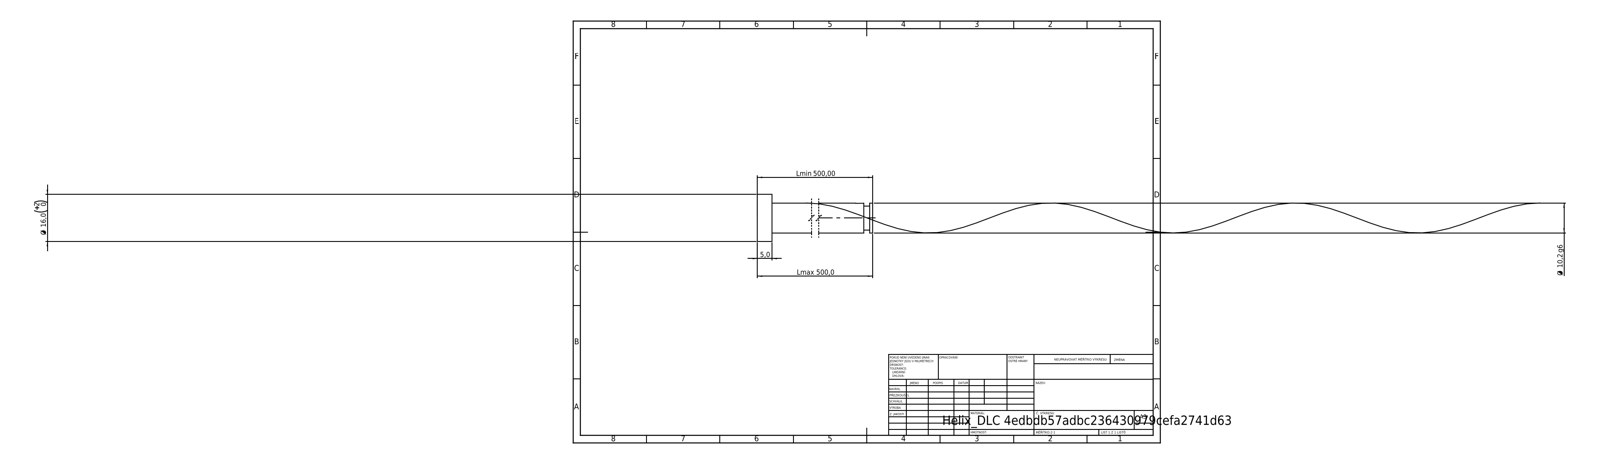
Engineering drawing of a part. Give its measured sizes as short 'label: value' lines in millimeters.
written by: SolidWorks 2019 (CONFIG_CONTROL_DESIGN)
unit: mm
bodies: 1 solid, 21 faces (6 planar, 14 cylindrical, 1 other)
size: 500 × 16 × 16
volume: 41 002 mm³; area: 16 825 mm²
bosses: 1× ⌀16, 1× ⌀10.2, 1× ⌀8.16
face distances: 5, 500, 495, 498.94, 493.94, 1.06, 496.9, 491.9, 2.04, 3.1
